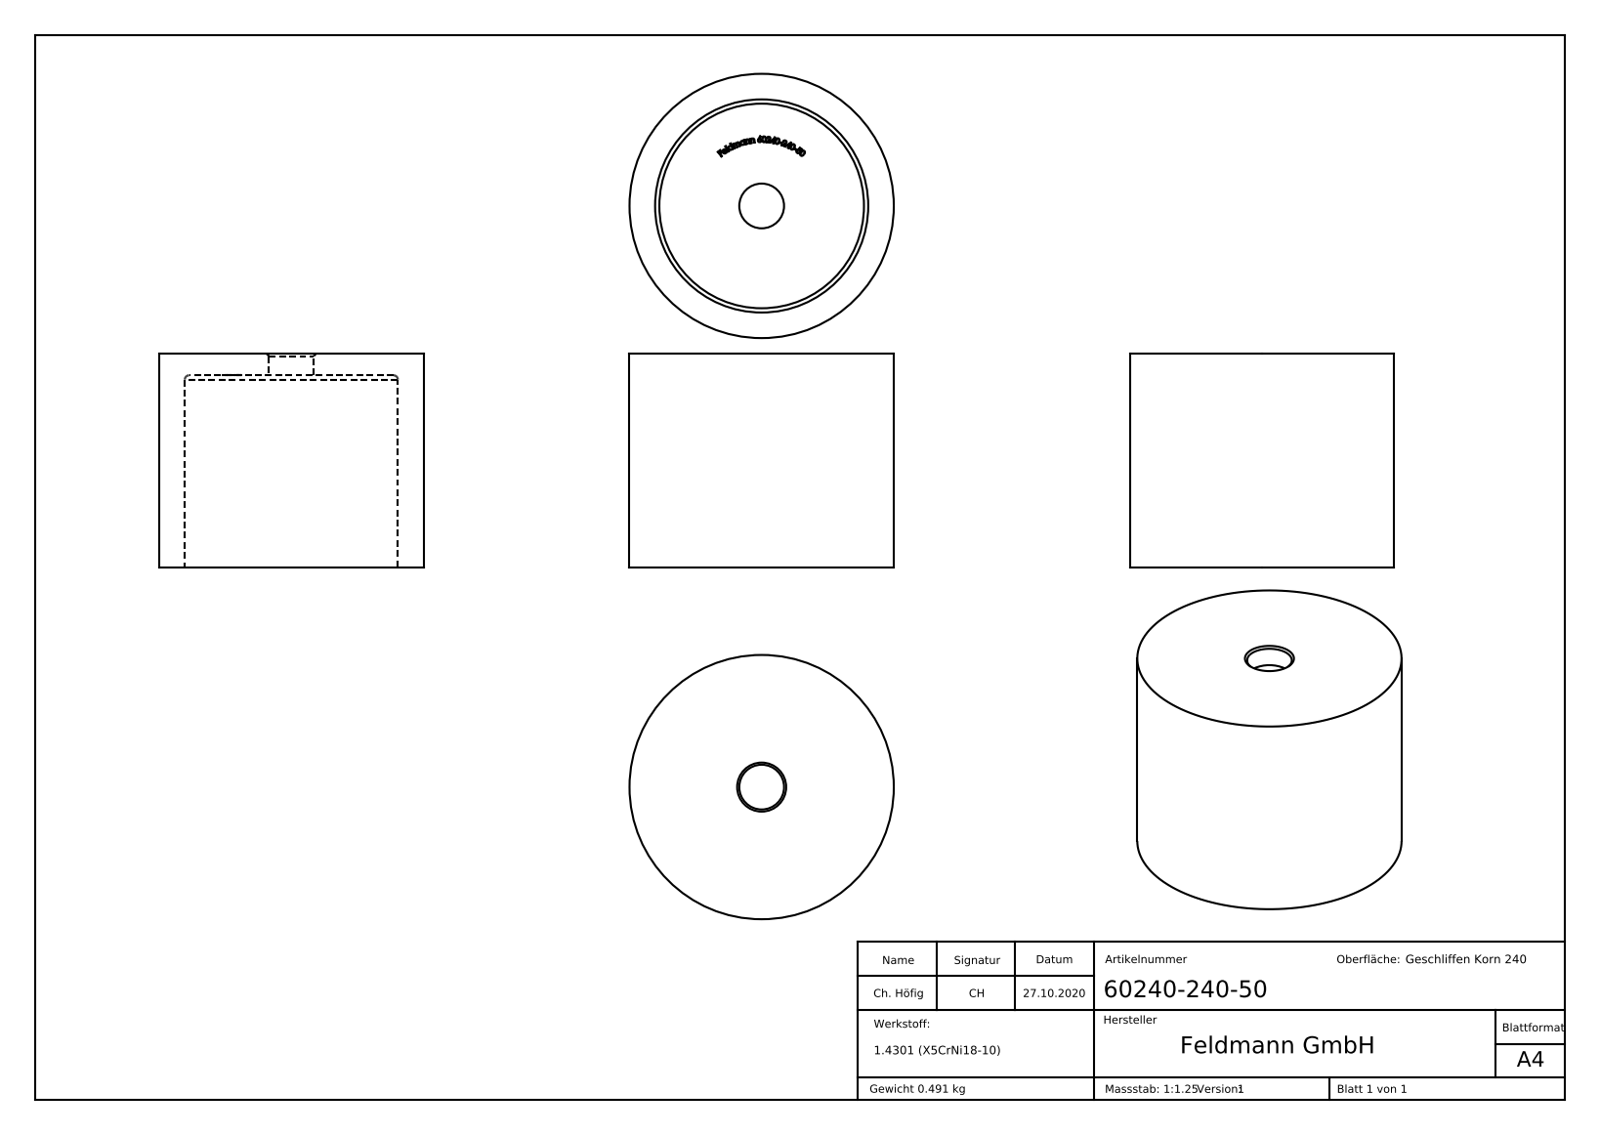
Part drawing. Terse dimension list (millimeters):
name: 60240-240-50
written by: SolidWorks 2018 (CONFIG_CONTROL_DESIGN)
unit: mm
bodies: 1 solid, 265 faces (142 planar, 6 cylindrical, 117 other)
size: 62 × 62 × 50
volume: 62 192 mm³; area: 22 771 mm²
holes: 1× ⌀10.5, 1× ⌀50
bosses: 1× ⌀62
face distances: 5, 45, 50, 45.1, 4.9, 0.54, 1.33, 0.73, 1.46, 0.67
